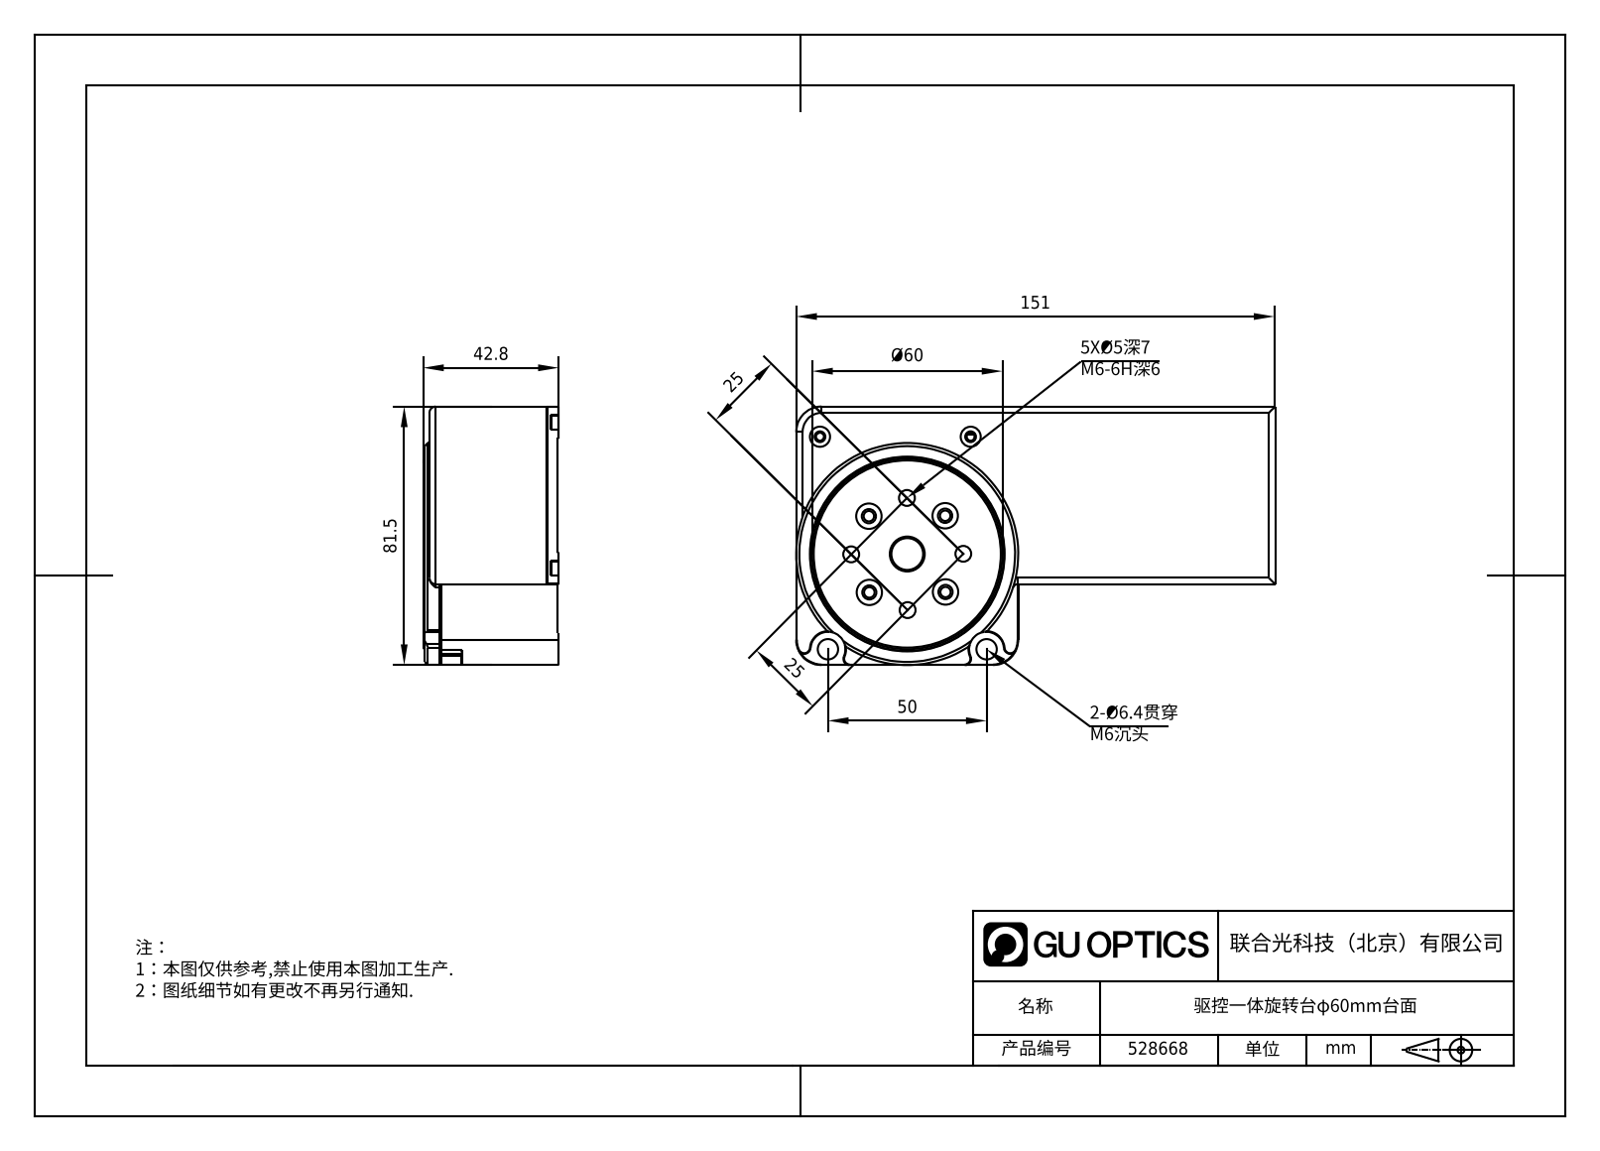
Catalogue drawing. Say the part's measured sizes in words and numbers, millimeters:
The part is named "528668". Its 3-D file was written by "SolidWorks 2020 (CONFIG_CONTROL_DESIGN)". It is 19 solids with 1383 faces: 433 planar, 684 cylindrical and 266 other. Overall it measures 151 by 81.5 by 42.8 millimeters. Its volume is 291 834 cubic millimeters and its surface area 123 696 square millimeters. Round holes: 22 of diameter 2.5, 17 of diameter 3.4, 13 of diameter 6.5, 8 of diameter 3.3, 8 of diameter 4.5, 8 of diameter 8, 4 of diameter 3, 4 of diameter 5, 3 of diameter 1.6, 3 of diameter 2, 3 of diameter 4.2, 3 of diameter 8.1. Round bosses or shafts: 1 of diameter 70, 1 of diameter 63, 1 of diameter 60, 1 of diameter 52, 1 of diameter 50.8, 1 of diameter 45, 1 of diameter 22, 1 of diameter 20. Partial cylindrical surfaces (rounded edges, fillets, slot ends): 24 of radius 2, 12 of radius 0.5, 6 of radius 3, 5 of radius 8, 4 of radius 3.25, 2 of radius 1, 2 of radius 1.75, 2 of radius 2.2. The main face-to-face distances are 3.5, 2, 37, 4, 35, 33.5, 3, 0.5, 35.5, 10. The hole center spacings are 21, 13.15, 15.37, 18, 18.38, 22.04, 25.46, 26.
